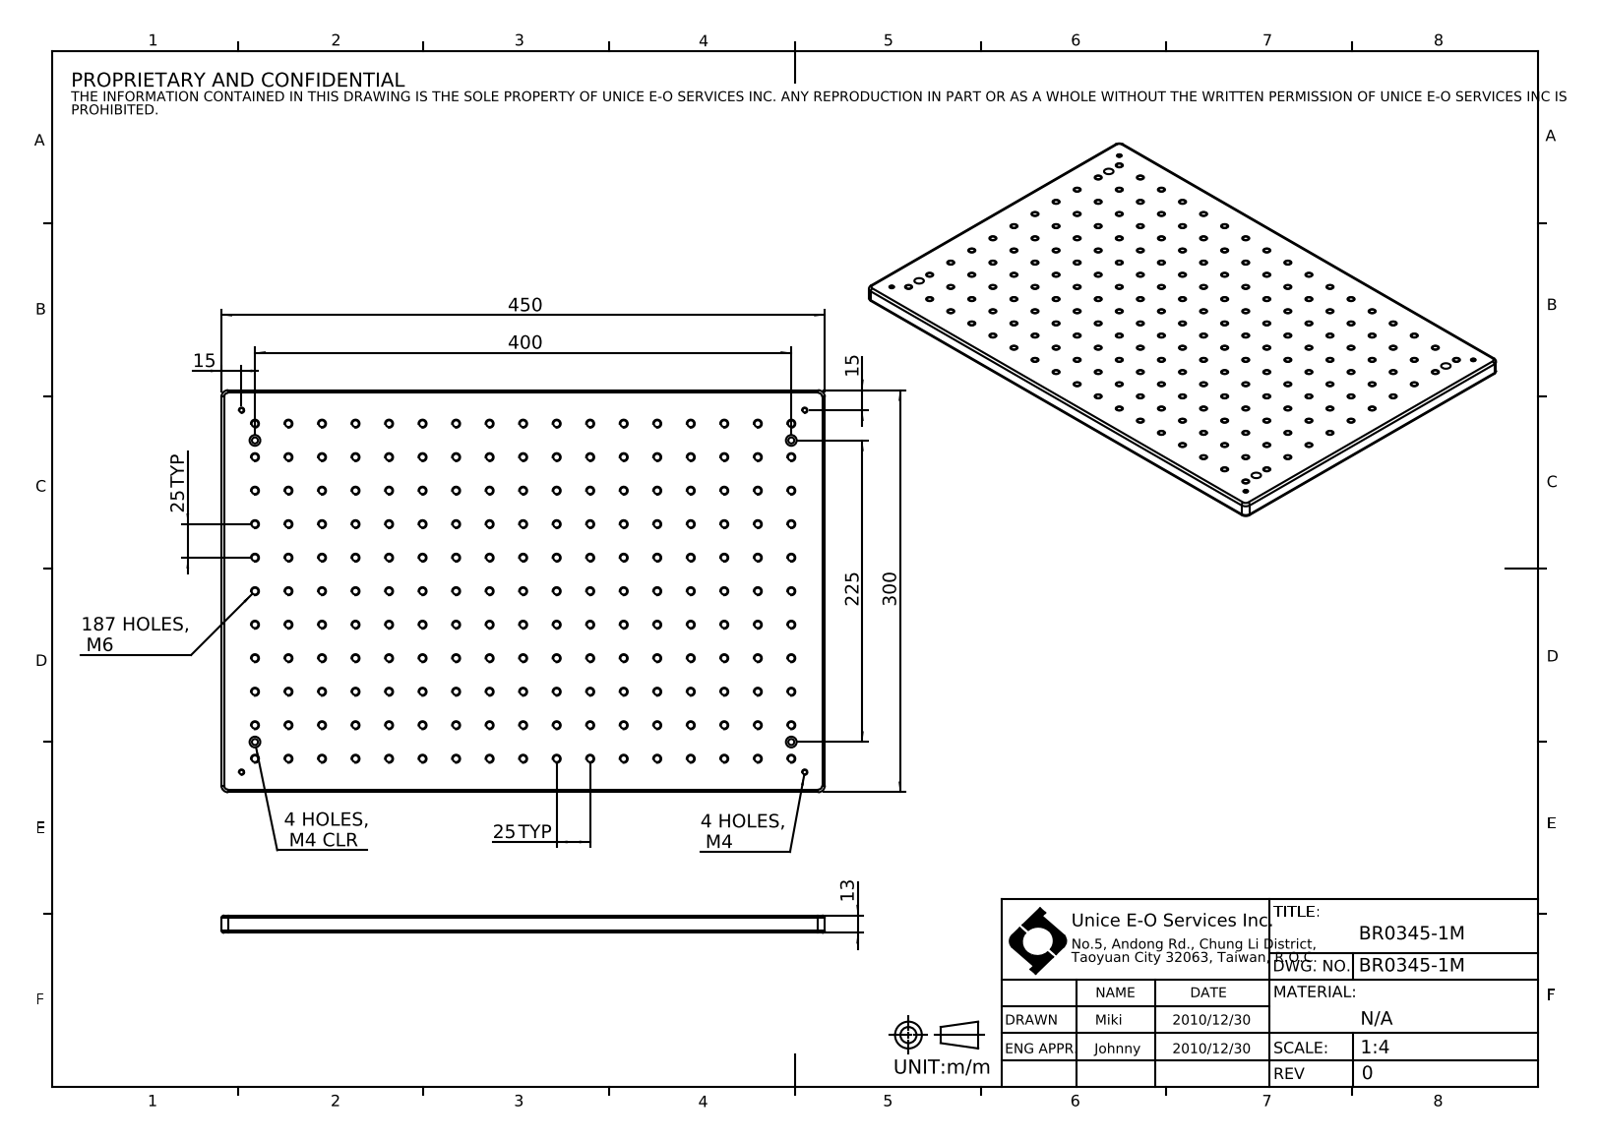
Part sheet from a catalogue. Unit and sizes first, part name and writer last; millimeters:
Units: millimetres
Overall size (bounding box): 450 × 300 × 13
Round holes (diameter × count): ⌀5 ×187, ⌀3.3 ×4, ⌀4.5 ×4, ⌀8 ×4
Partial cylindrical surfaces — rounded edges, fillets, slot ends (radius × count): R2 ×8, R5 ×4
Main face-to-face distances: 13, 300, 450, 7, 6
Hole centre spacings: 25, 50, 75, 125, 100, 251.25, 254.95, 250
Volume: 1 702 000 mm³ · Surface area: 318 966 mm²
Bodies: 1 solid, 428 faces (10 planar, 410 cylindrical, 8 other)
Part name (STEP PRODUCT): BR0345-1M
STEP written by: SolidWorks 2016 (CONFIG_CONTROL_DESIGN)
